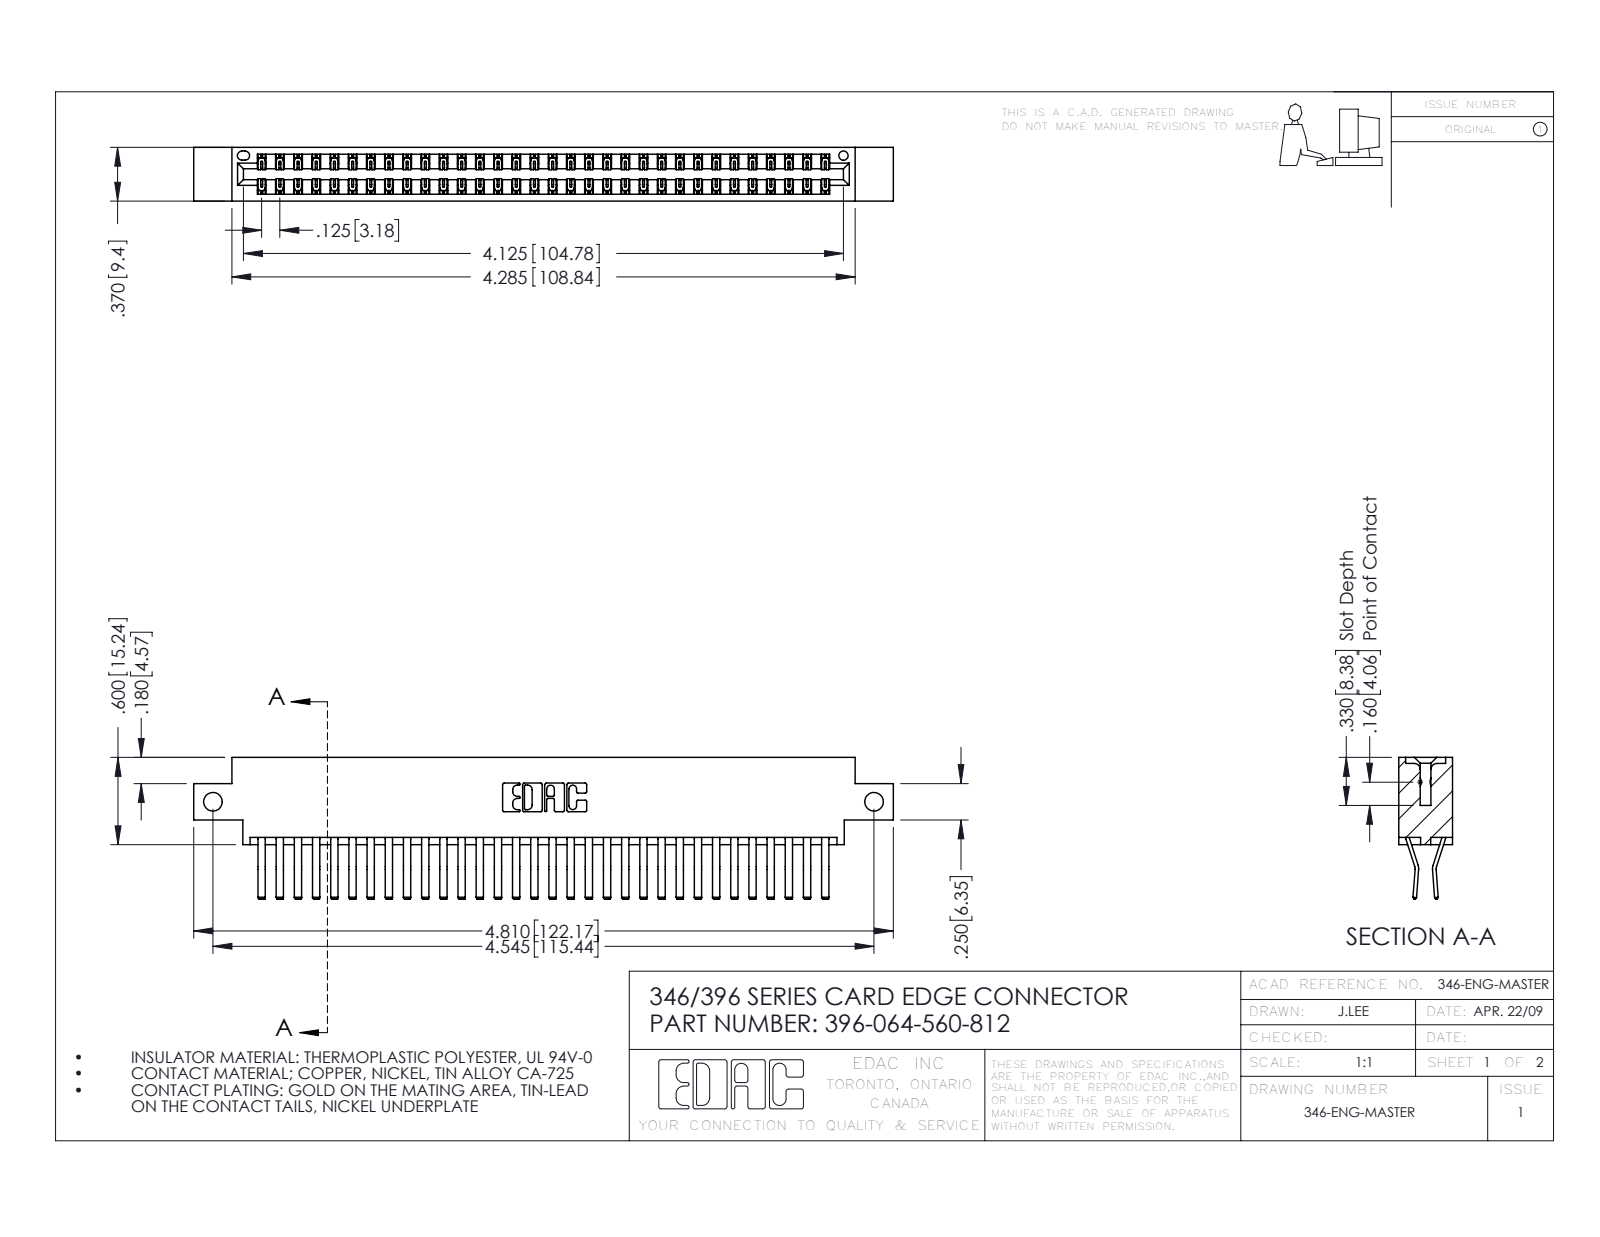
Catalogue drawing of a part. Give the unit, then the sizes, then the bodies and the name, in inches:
Units: inches
Overall size (bounding box): 4.81 × 0.975 × 0.37
Round holes (diameter × count): ⌀0.128 ×2, ⌀0.064 ×1
Partial cylindrical surfaces — rounded edges, fillets, slot ends (radius × count): R0.006 ×96, R0.01 ×22, R0.007 ×6, R0.031 ×6, R0.026 ×3, R0.01 ×2, R0.014 ×2, R0.022 ×2
Main face-to-face distances: 0.048, 0.322, 0.37, 0.025, 0.25, 0.072, 0.298, 0.275, 0.148, 0.222
Hole centre spacings: 4.545
Volume: 0.733 in³ · Surface area: 27.15 in²
Bodies: 65 solids, 3582 faces (2320 planar, 1262 cylindrical, 0 other)
Part name (STEP PRODUCT): 396-064-560-812; 345-292-001_560 Tail; 346 Part_0.170 Offset - Side Mount
STEP written by: SolidWorks 2016 (CONFIG_CONTROL_DESIGN)
